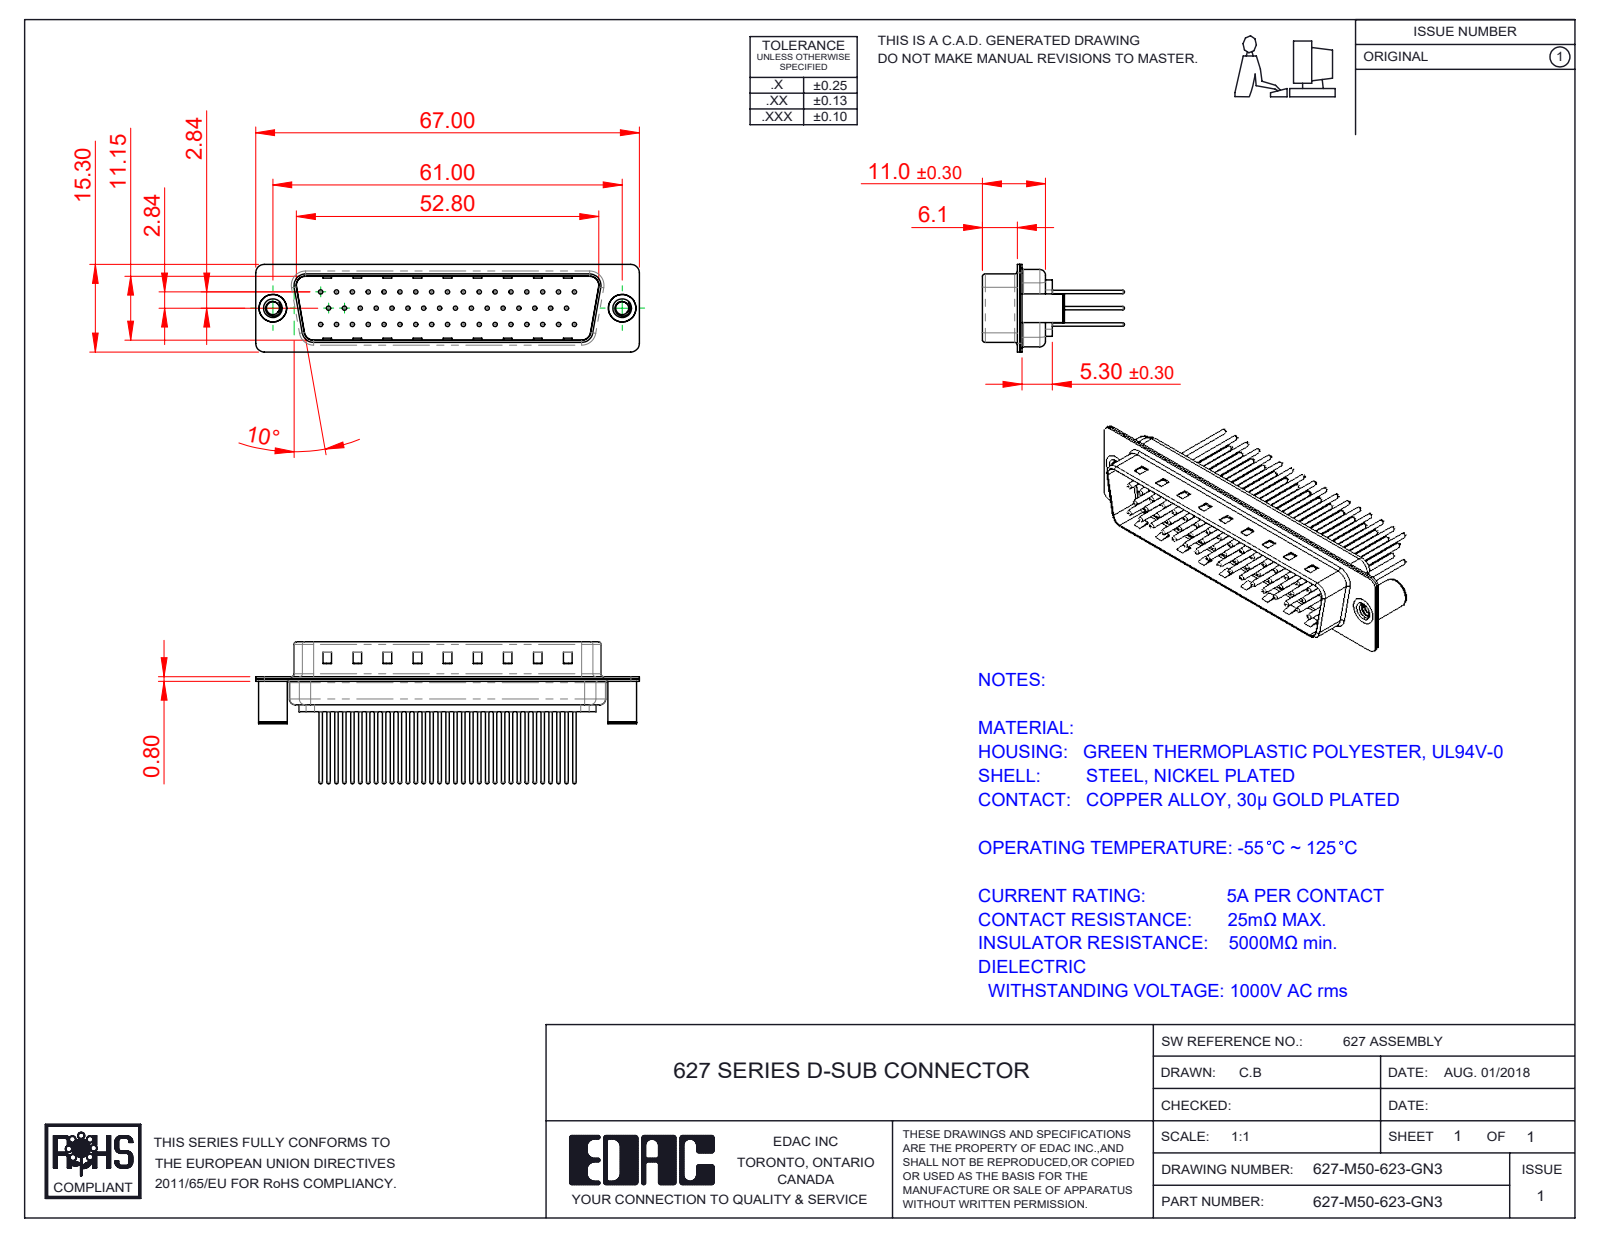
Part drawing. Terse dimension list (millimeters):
name: 627M Housing_50 Contacts; 627M Shell Front_50 Contacts; 627M Contact Row 2_23; 627M Shell Rear_50 Contacts (+4 more)
written by: SolidWorks 2020 (CONFIG_CONTROL_DESIGN)
unit: mm
bodies: 55 solids, 2296 faces (553 planar, 865 cylindrical, 878 other)
size: 67 × 24.77 × 15.3
volume: 4 745 mm³; area: 11 605 mm²
holes: 50× ⌀0.75, 50× ⌀1.6, 50× ⌀2, 2× ⌀2.26, 2× ⌀3.26, 2× ⌀4, 2× ⌀4.8
bosses: 50× ⌀1.5, 50× ⌀0.6, 2× ⌀5, 2× ⌀4.9
rounds: 16× R1.5, 12× R2, 8× R0.5, 8× R1.6, 4× R0.25, 4× R0.6, 4× R0.65, 4× R0.9
face distances: 0.4, 11.55, 5.7, 6.1, 0.78, 0.77, 12.33, 5.3, 12.32, 13.1
hole spacings: 3.16, 2.77, 5.54, 8.31, 11.08, 13.85, 16.62, 5.03
